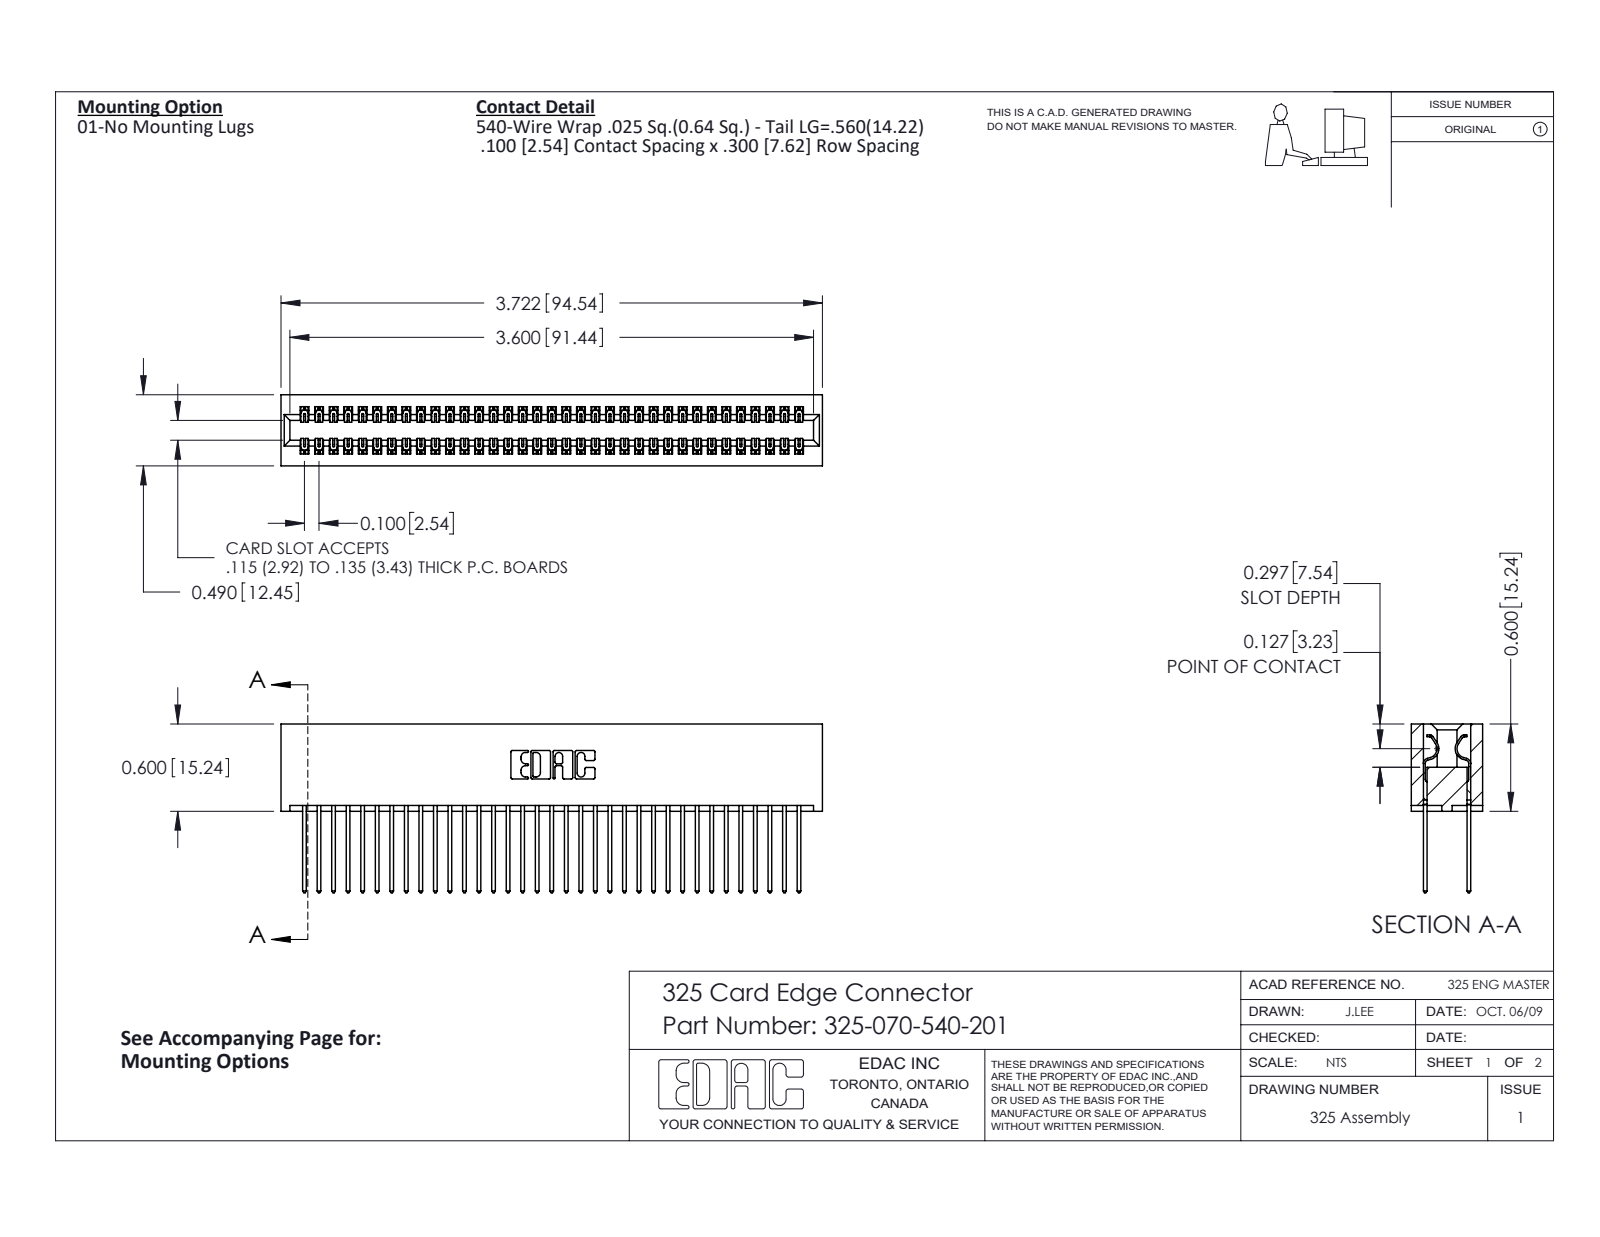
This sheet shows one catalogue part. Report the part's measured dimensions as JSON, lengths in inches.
{"part_name": "325-292-001_325-293-140; 325 Part_Lugless; 325-070-540-201", "step_written_by": "SolidWorks 2016 (CONFIG_CONTROL_DESIGN)", "units": "inches", "bodies": {"solids": 71, "faces": 3746, "planar": 2586, "cylindrical": 1160, "other": 0}, "overall_size": [3.722, 1.16, 0.49], "volume_in3": 0.794, "surface_area_in2": 27.14, "partial_cylinders_radius": [[0.006, 105], [0.01, 70], [0.01, 22], [0.007, 6], [0.031, 6], [0.026, 3], [0.014, 2], [0.022, 2]], "face_to_face_distances": [0.083, 0.407, 0.3, 0.107, 0.383, 0.025, 0.325, 0.49, 0.275, 0.56]}
